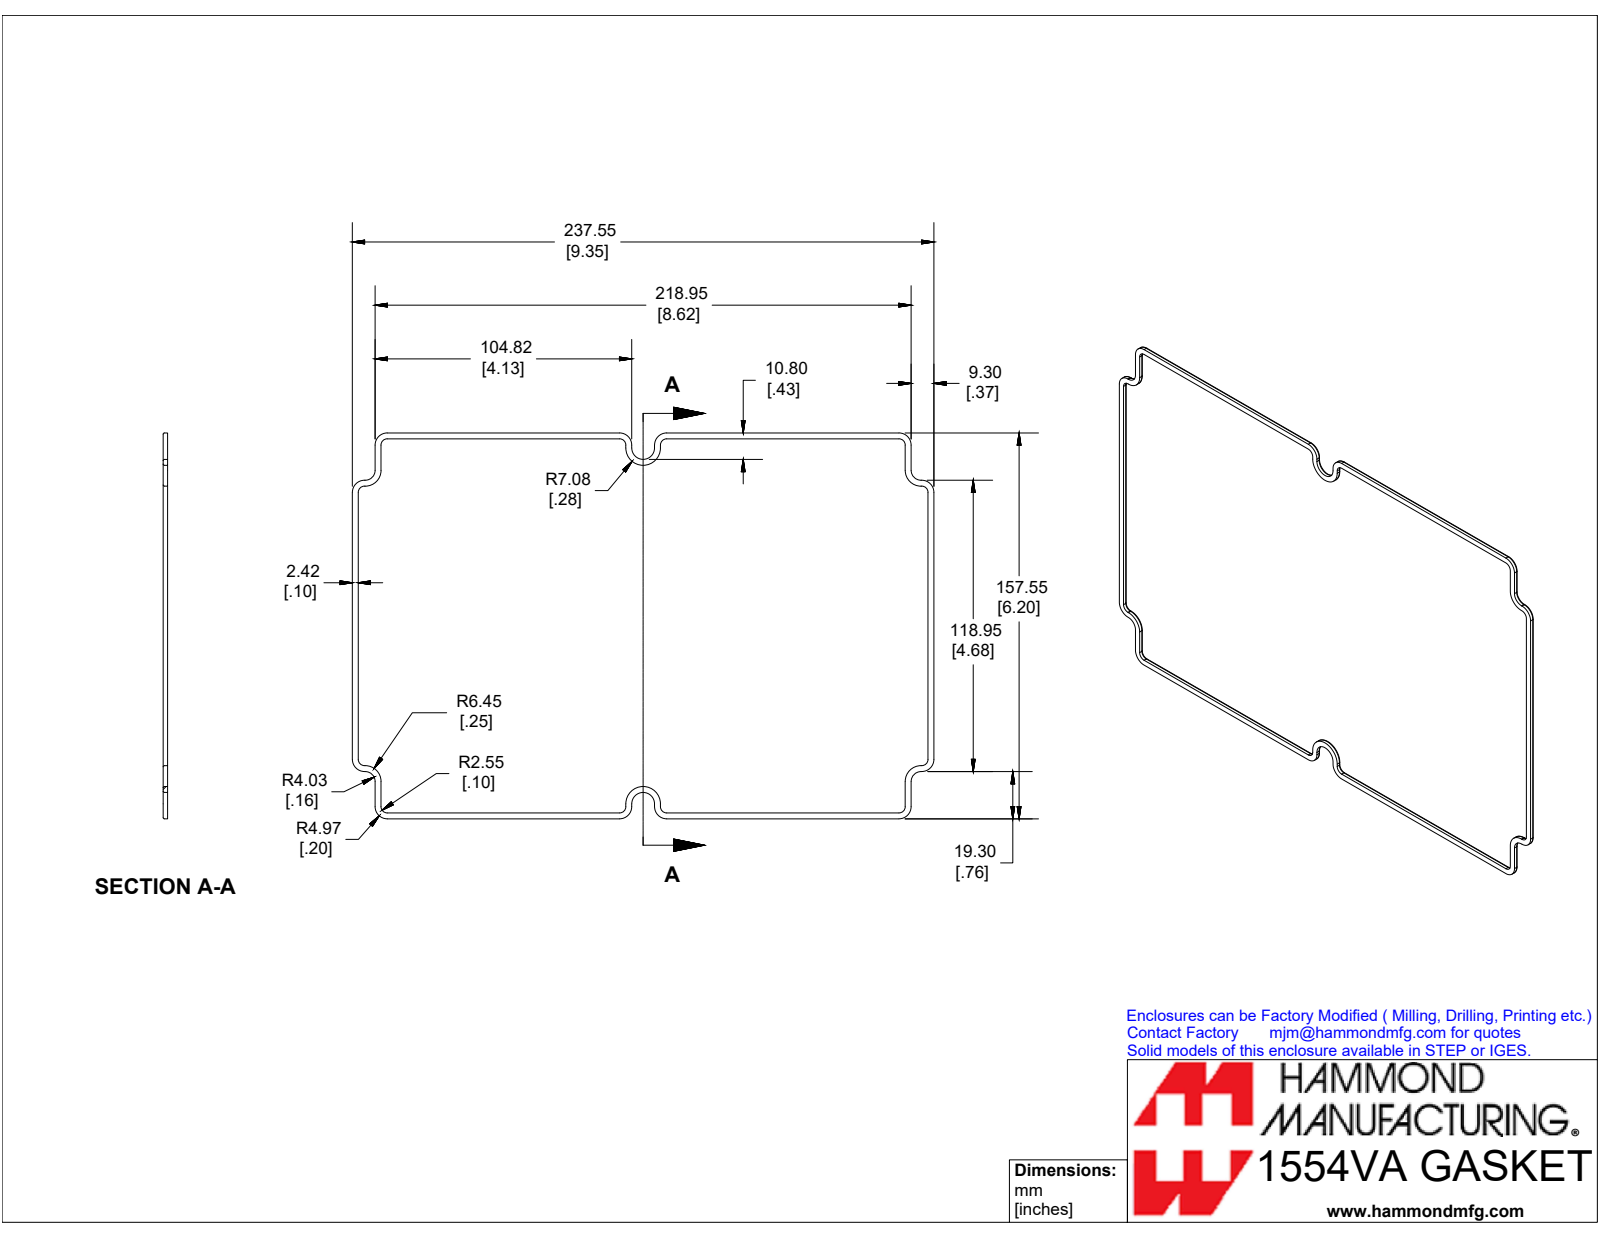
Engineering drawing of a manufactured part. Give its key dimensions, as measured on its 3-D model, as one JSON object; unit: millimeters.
{"part_name": "1554VAGASKET", "step_written_by": "SolidWorks 2019 (CONFIG_CONTROL_DESIGN)", "units": "millimeters", "bodies": {"solids": 1, "faces": 146, "planar": 38, "cylindrical": 72, "other": 36}, "overall_size": [237.5, 157.5, 1.8], "volume_mm3": 3310, "surface_area_mm2": 6259, "partial_cylinders_radius": [[0.5, 20], [2.5, 12], [5, 12], [4, 4], [6.5, 4], [4.7, 2], [7.1, 2]], "face_to_face_distances": [1.8, 2.4, 155.1, 235.1, 157.5, 152.7, 237.5, 232.7, 9.3, 225.8]}
